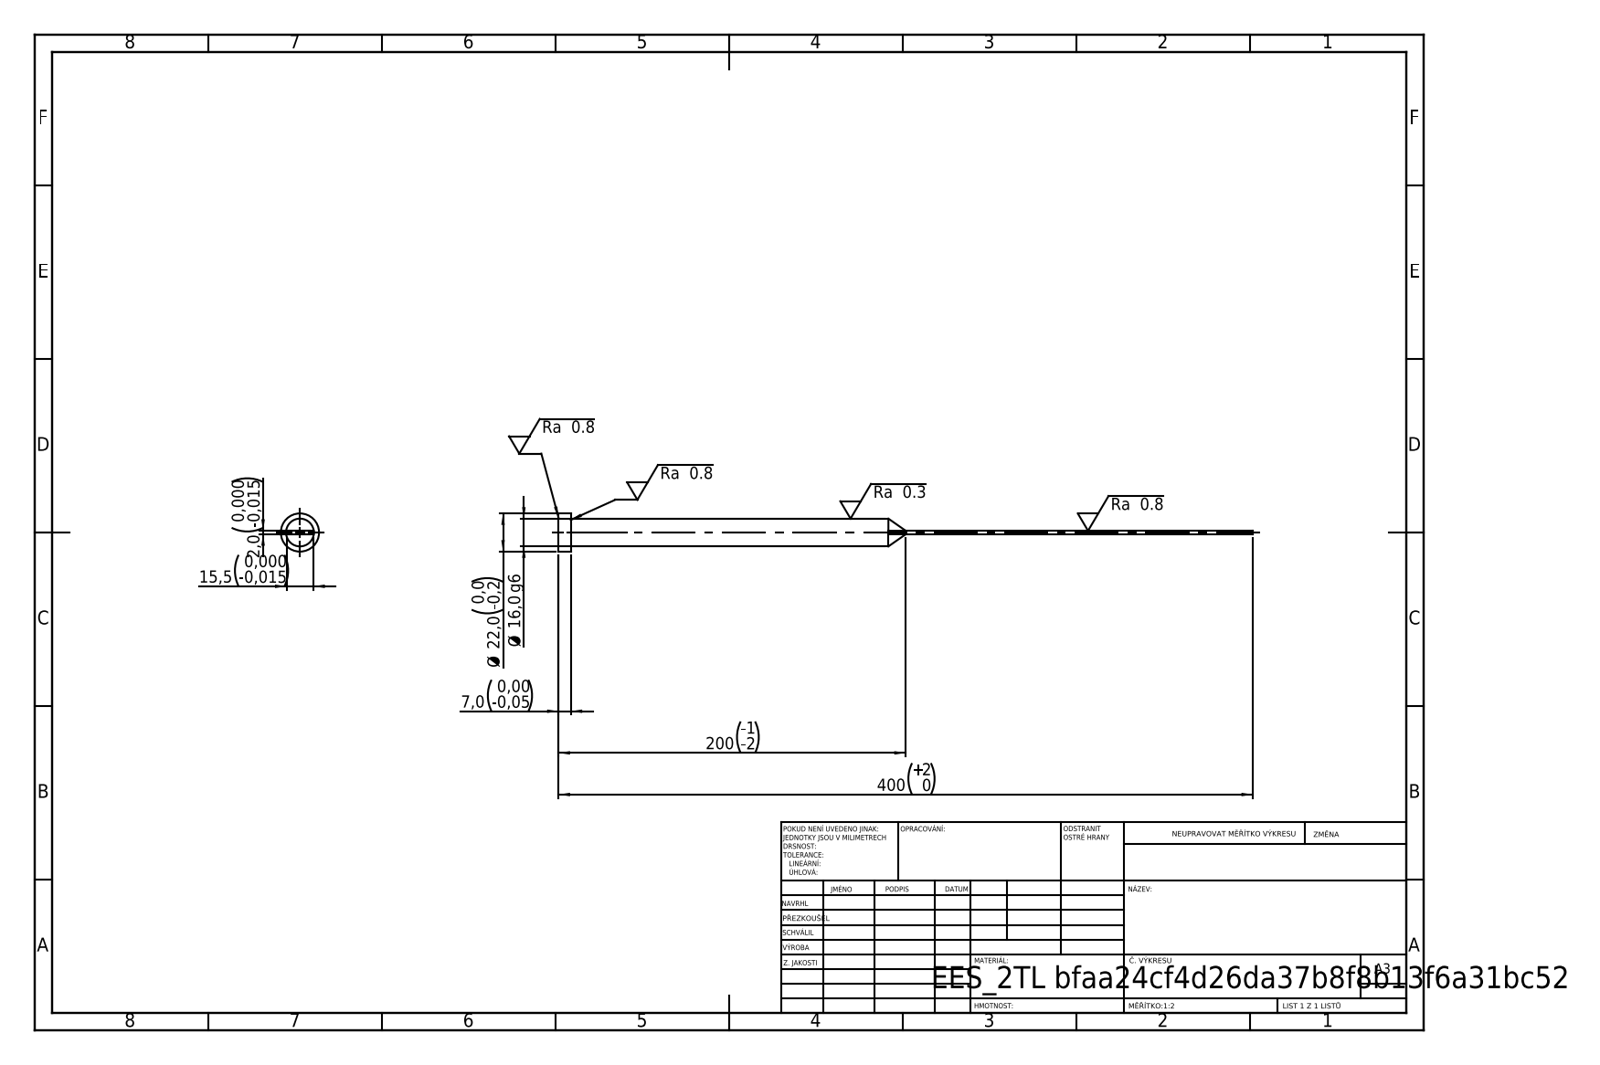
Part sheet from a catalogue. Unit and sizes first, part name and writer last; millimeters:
Units: millimetres
Overall size (bounding box): 400 × 22 × 22
Round bosses / shafts (diameter × count): ⌀22 ×1, ⌀16 ×1
Main face-to-face distances: 2, 15.5, 7, 400, 393
Volume: 46 747 mm³ · Surface area: 17 720 mm²
Bodies: 1 solid, 15 faces (7 planar, 4 cylindrical, 4 other)
STEP written by: SolidWorks 2019 (CONFIG_CONTROL_DESIGN)
